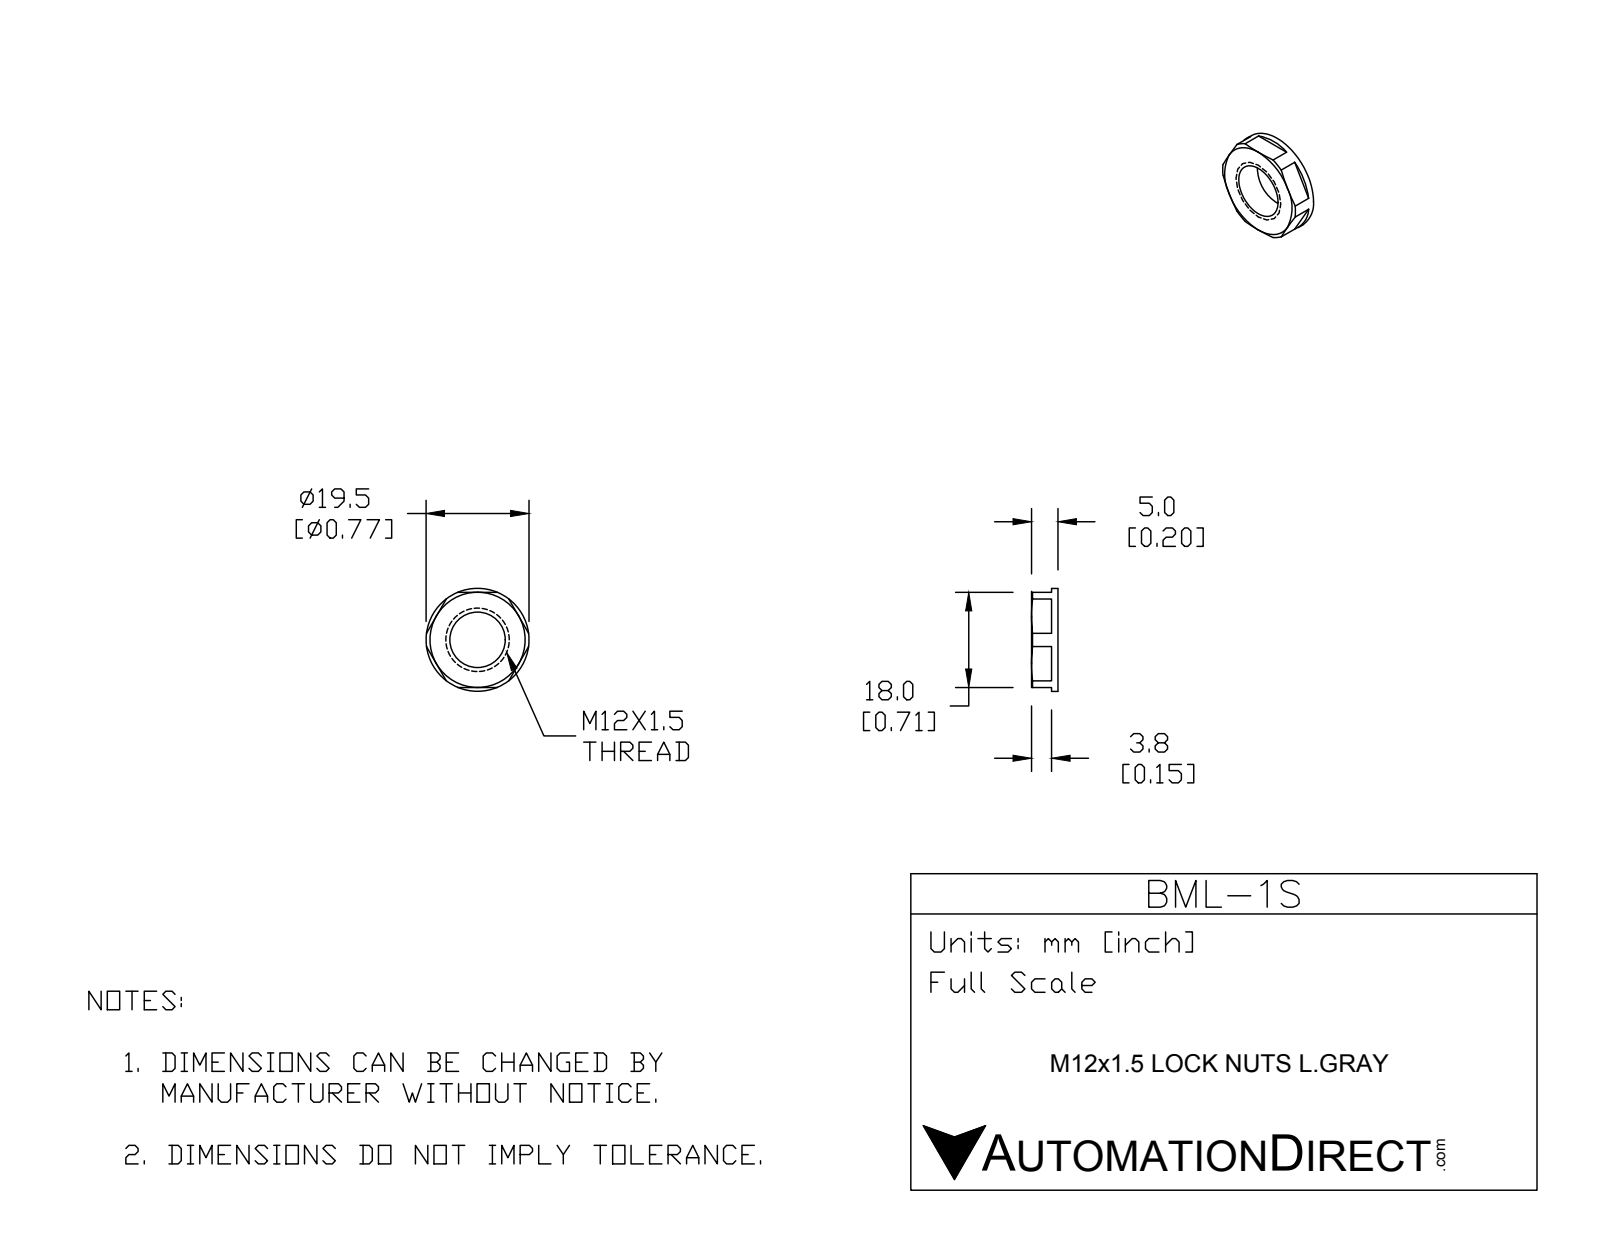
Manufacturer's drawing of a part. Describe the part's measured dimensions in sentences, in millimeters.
The part is named "BML-1S". Its 3-D file was written by "SolidWorks 2015 (CONFIG_CONTROL_DESIGN)". It is 1 solid with 34 faces: 17 planar, 10 cylindrical and 7 other. Overall it measures 19.5 by 19.5 by 5 millimeters. Its volume is 971 cubic millimeters and its surface area 890 square millimeters. Round holes: 3 of diameter 1.5, 1 of diameter 10.5. Round bosses or shafts: 1 of diameter 19.5. The main face-to-face distances are 5, 18, 1.2, 3.8, 0.9, 4.7. The hole center spacings are 8.3, 14.38.
